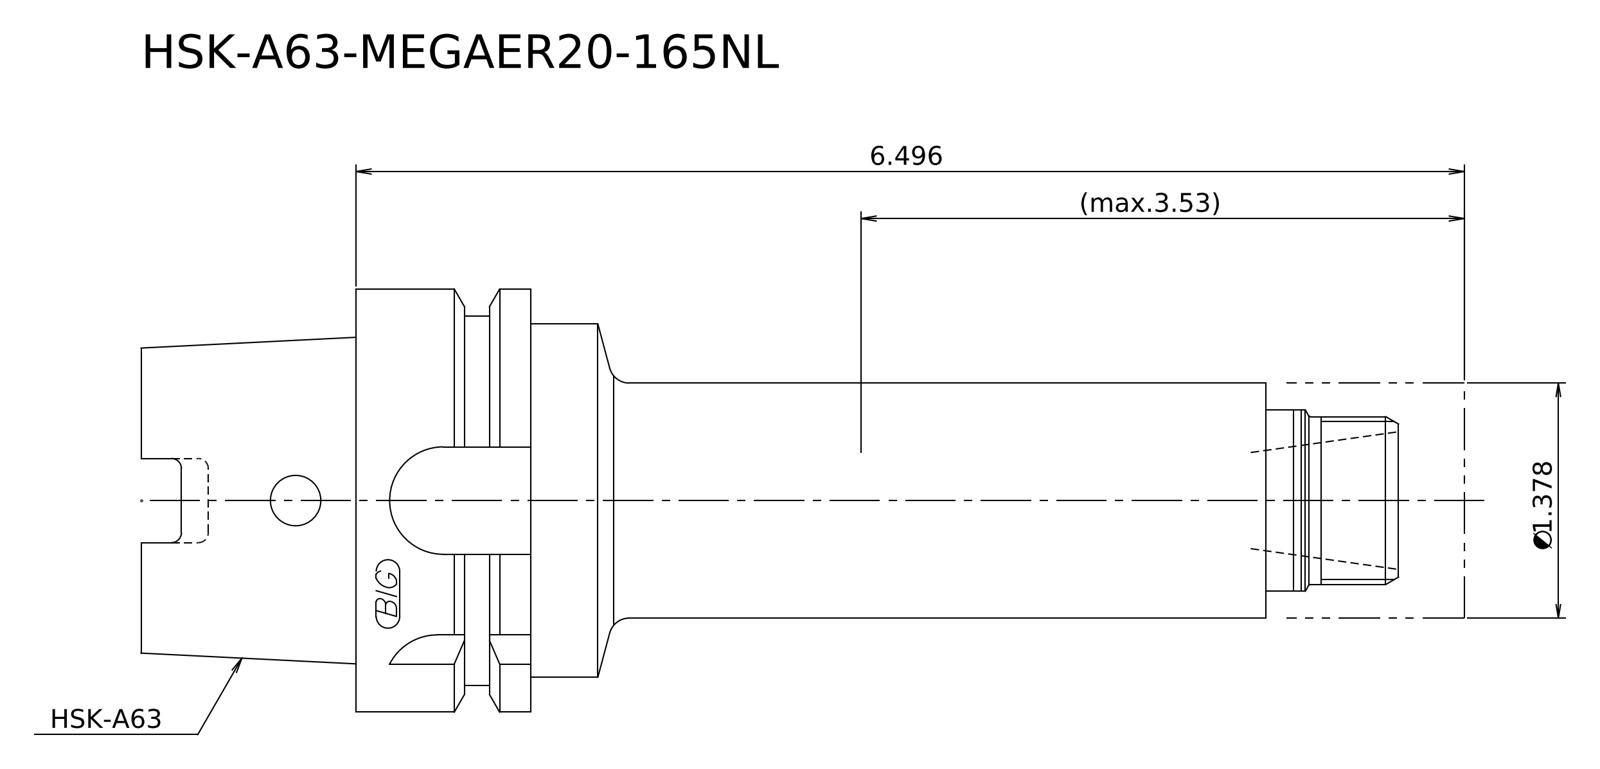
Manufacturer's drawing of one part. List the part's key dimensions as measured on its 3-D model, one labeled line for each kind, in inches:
STEP written by: Kubotek KeyCreator 2011 V10.0.2 (22737) (automotive_design)
Units: inches
Bodies: 2 solids, 23 faces (9 planar, 8 cylindrical, 6 other)
Overall size (bounding box): 7.756 × 2.48 × 2.48
Volume: 17.62 in³ · Surface area: 54.85 in²
Round bosses / shafts (diameter × count): ⌀2.48 ×1, ⌀2.165 ×1, ⌀2.071 ×1, ⌀1.378 ×1, ⌀1.063 ×1, ⌀0.984 ×1
Main face-to-face distances: 1.26, 5.453, 6.713, 1.043, 6.496, 7.756, 5.472, 4.429, 1.024, 2.283
